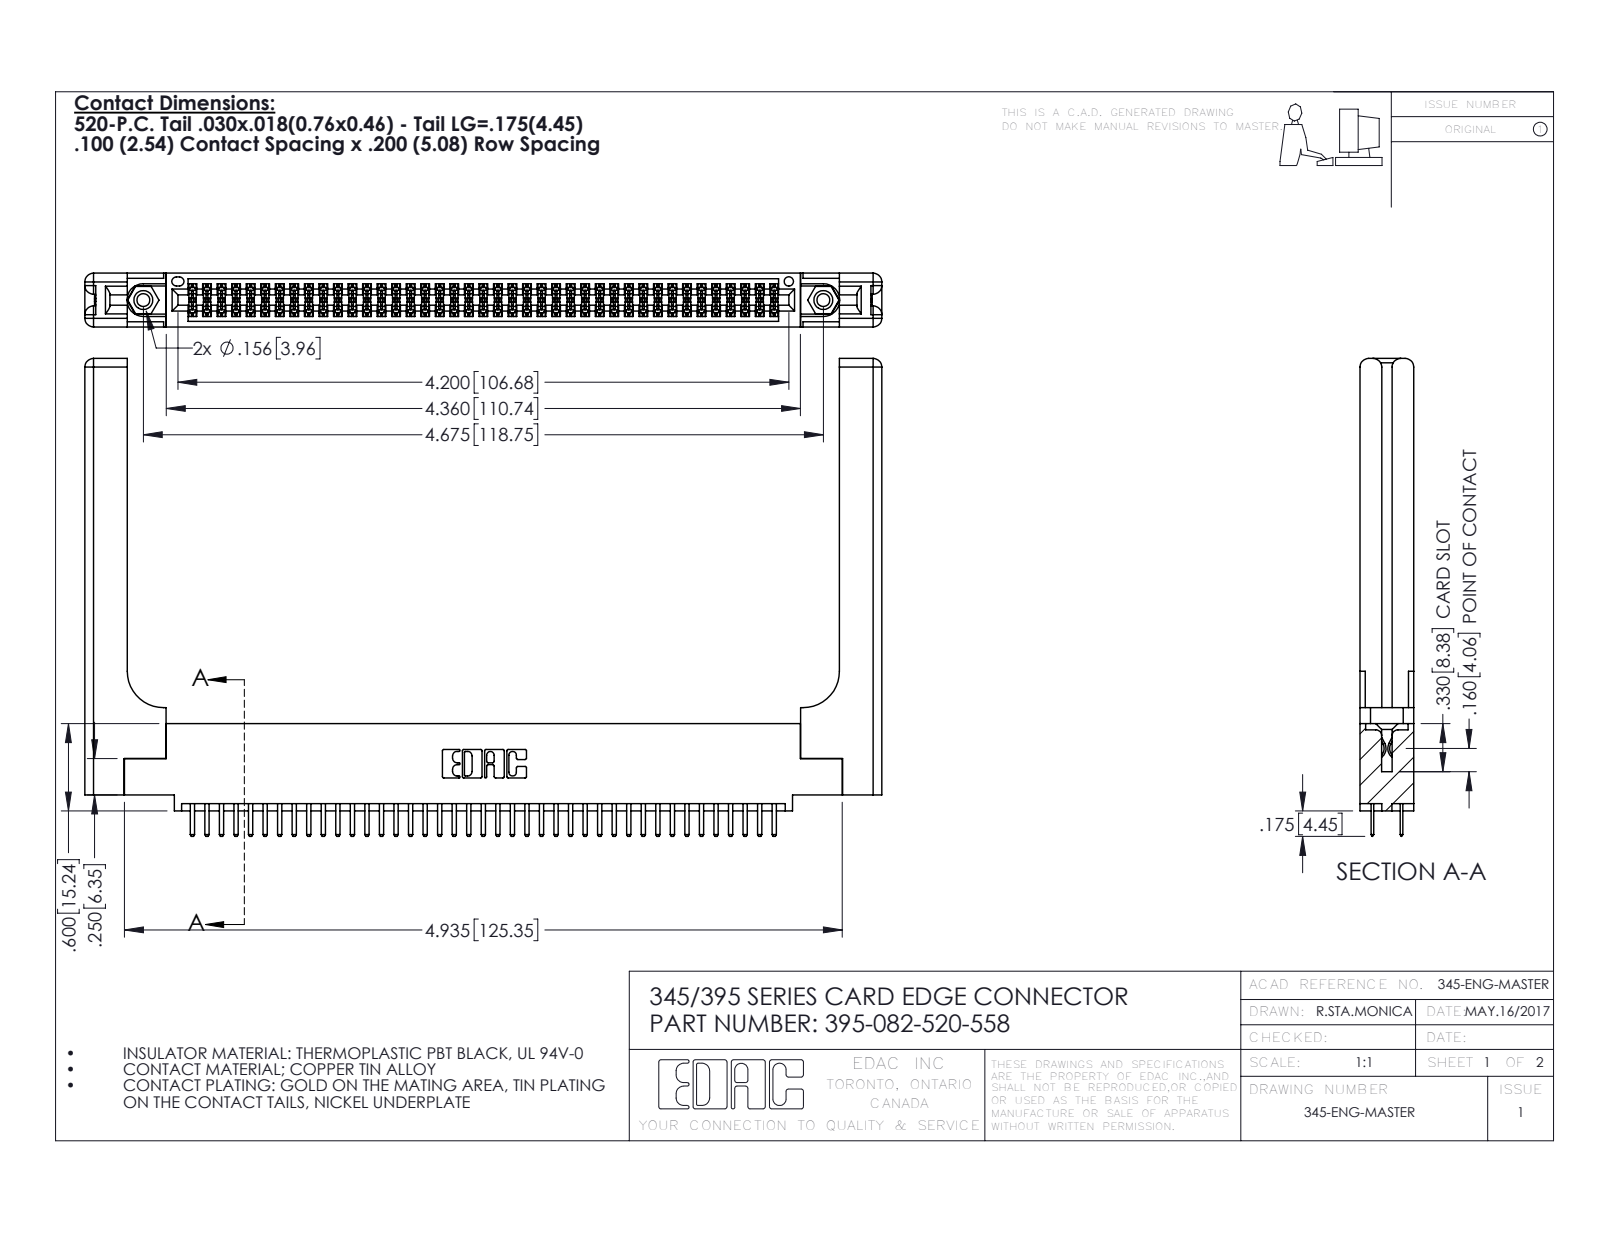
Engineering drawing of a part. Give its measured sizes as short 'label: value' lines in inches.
name: 345-220-058_345-220-058; 395-082-520-558; 345-292-001_345-293-120; 345-250-001_345-250-001-102 (+1 more)
written by: SolidWorks 2016 (CONFIG_CONTROL_DESIGN)
unit: in
bodies: 87 solids, 4814 faces (3102 planar, 1652 cylindrical, 60 other)
size: 5.479 × 3.285 × 0.37
volume: 1.335 in³; area: 38.54 in²
holes: 2× ⌀0.089, 2× ⌀0.125, 2× ⌀0.156, 1× ⌀0.064
bosses: 2× ⌀0.155
rounds: 123× R0.006, 86× R0.01, 22× R0.01, 16× R0.06, 6× R0.007, 6× R0.031, 3× R0.026, 2× R0.014
face distances: 0.37, 0.072, 0.298, 0.2, 0.098, 0.272, 0.025, 0.225, 0.148, 0.15
hole spacings: 0.27, 4.439, 4.675
